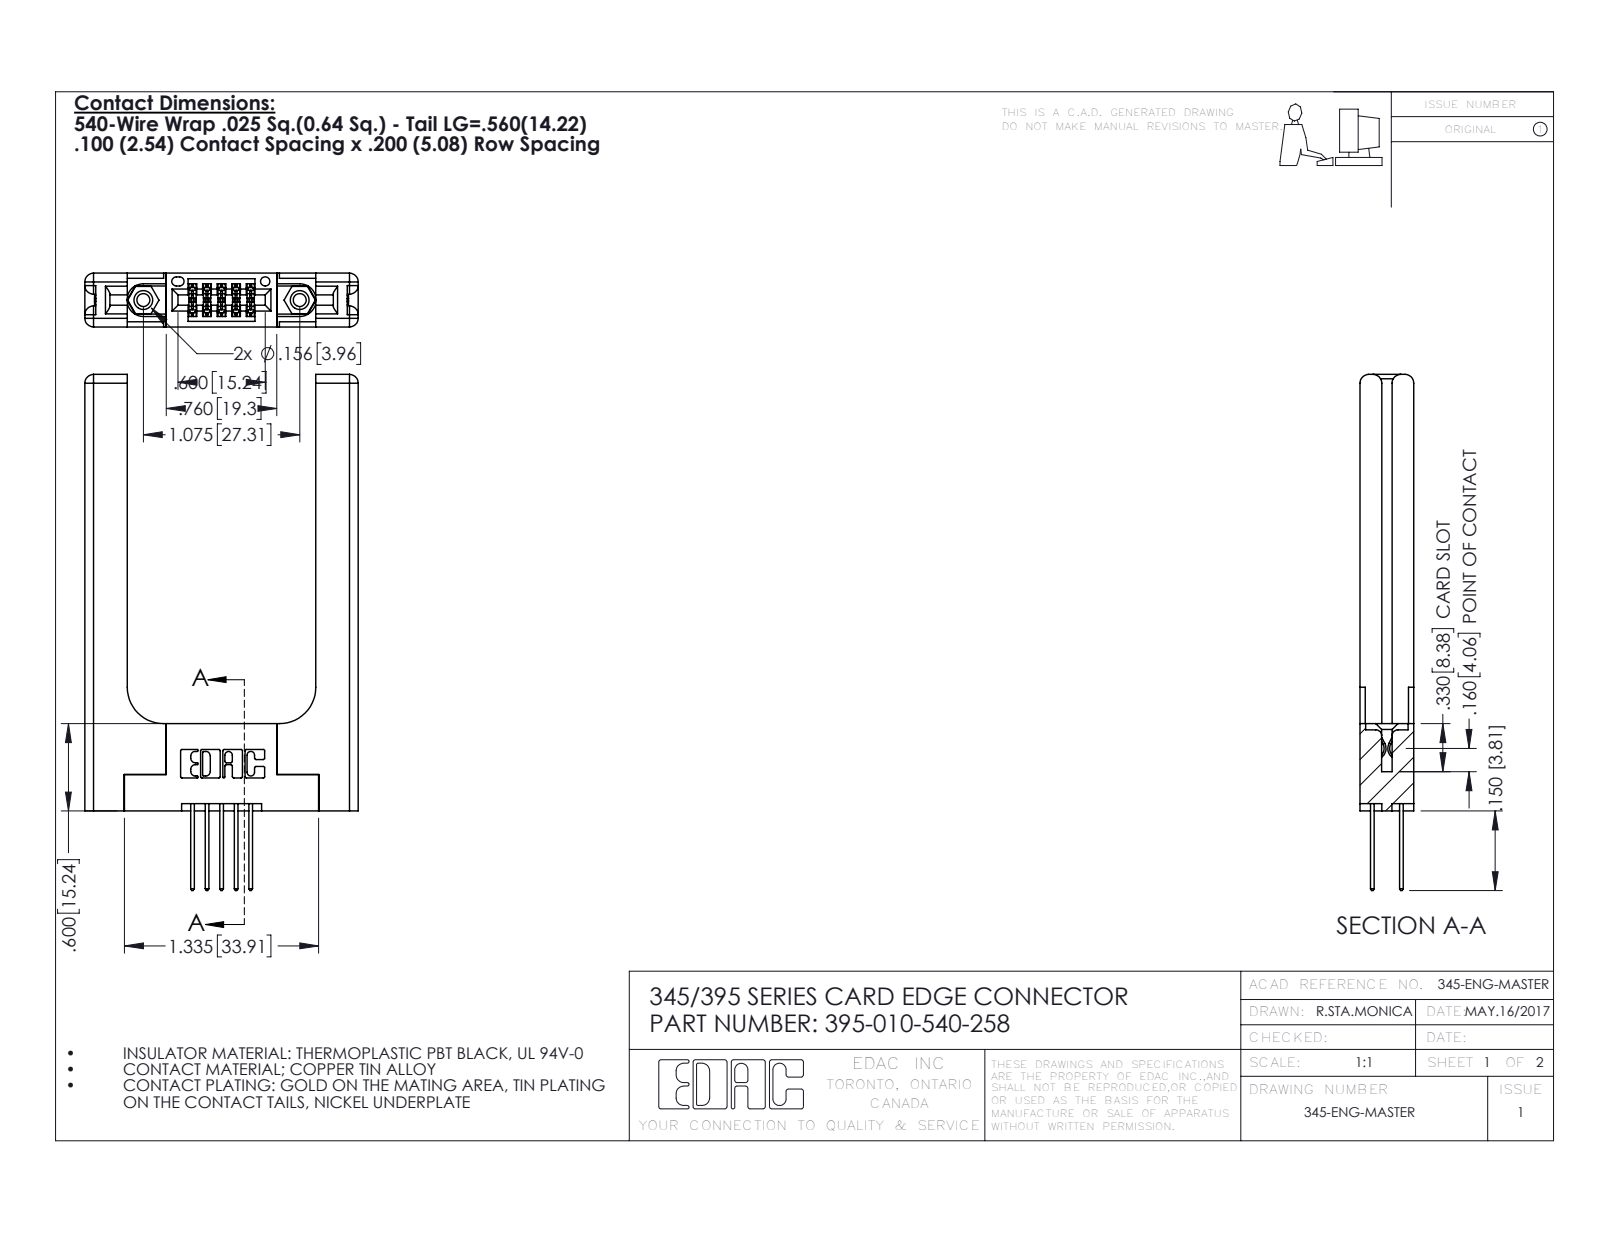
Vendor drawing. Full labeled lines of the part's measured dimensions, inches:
Part name (STEP PRODUCT): 345-220-058_345-220-058; 345 Part_Flush Mounting Lugs - 0.156 Dia-TH; 395-010-540-258; 345-292-001_345-293-140 (+1 more)
STEP written by: SolidWorks 2016 (CONFIG_CONTROL_DESIGN)
Units: inches
Bodies: 15 solids, 882 faces (558 planar, 264 cylindrical, 60 other)
Overall size (bounding box): 3.547 × 1.879 × 0.37
Volume: 0.781 in³ · Surface area: 16.93 in²
Round holes (diameter × count): ⌀0.089 ×2, ⌀0.125 ×2, ⌀0.156 ×2, ⌀0.064 ×1
Round bosses / shafts (diameter × count): ⌀0.155 ×2
Partial cylindrical surfaces — rounded edges, fillets, slot ends (radius × count): R0.01 ×22, R0.06 ×16, R0.006 ×15, R0.01 ×10, R0.007 ×6, R0.031 ×6, R0.026 ×3, R0.014 ×2
Main face-to-face distances: 0.37, 0.15, 0.22, 0.072, 0.077, 0.148, 0.298, 1.296, 0.2, 0.071
Hole centre spacings: 0.27, 0.847, 1.075
